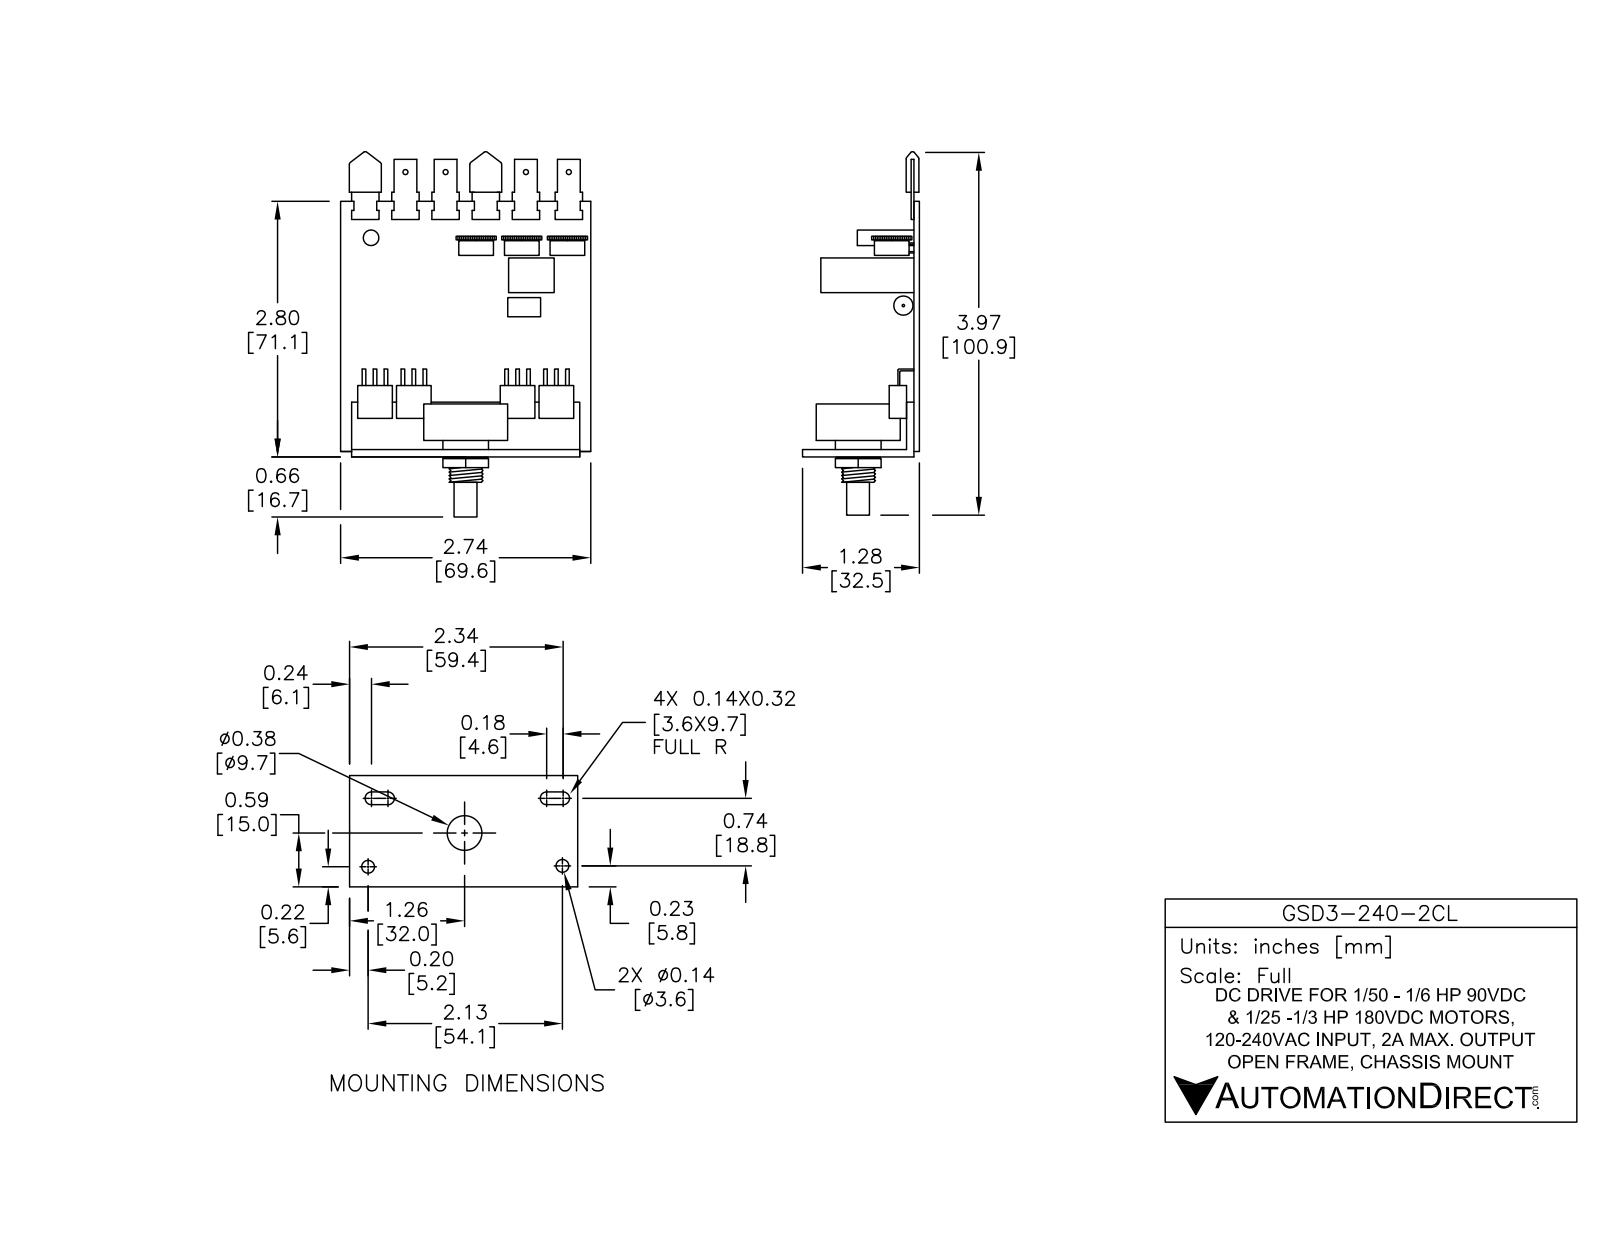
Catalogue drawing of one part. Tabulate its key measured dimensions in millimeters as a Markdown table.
| quantity | value |
| --- | --- |
| part name | Q5; RES_1_2WATT_VERTICAL_3.05S-3.05D-10.5H; HDRAD43A; DIOM_SMA (+7 more) |
| STEP written by | SolidWorks 2014 (AUTOMOTIVE_DESIGN) |
| units | millimeters |
| bodies | 107 solids, 3277 faces (2062 planar, 1023 cylindrical, 192 other) |
| overall size | 97.7 × 69.4 × 34.7 |
| volume | 29 560 mm³ |
| surface area | 31 520 mm² |
| round holes (diameter × count) | 0.7 × 22, 1.3 × 18, 0.8 × 15, 1.1 × 14, 1.2 × 14, 1.7 × 11, 3.6 × 7, 1 × 6, 2 × 4, 2.8 × 4, 3.7 × 4, 1.2 × 3 |
| round bosses / shafts (diameter × count) | 0.6 × 8, 0.7 × 6, 0.6 × 6, 6.4 × 5, 4 × 4, 9 × 3, 2.7 × 3, 1.3 × 3 |
| partial cylindrical surfaces (radius × count) | 0.1 × 48, 0.6 × 21, 1.3 × 12, 0.5 × 8, 1 × 4, 1.8 × 4, 2.3 × 4, 5.7 × 3 |
| main face-to-face distances | 1.6, 2, 3.6, 0.9, 2.5, 1.1, 6.7, 12.7, 8.3, 12.6 |
| hole center spacings | 3.8, 7.6, 9.4, 11.5, 14.7, 3.8, 5.9, 7 |
